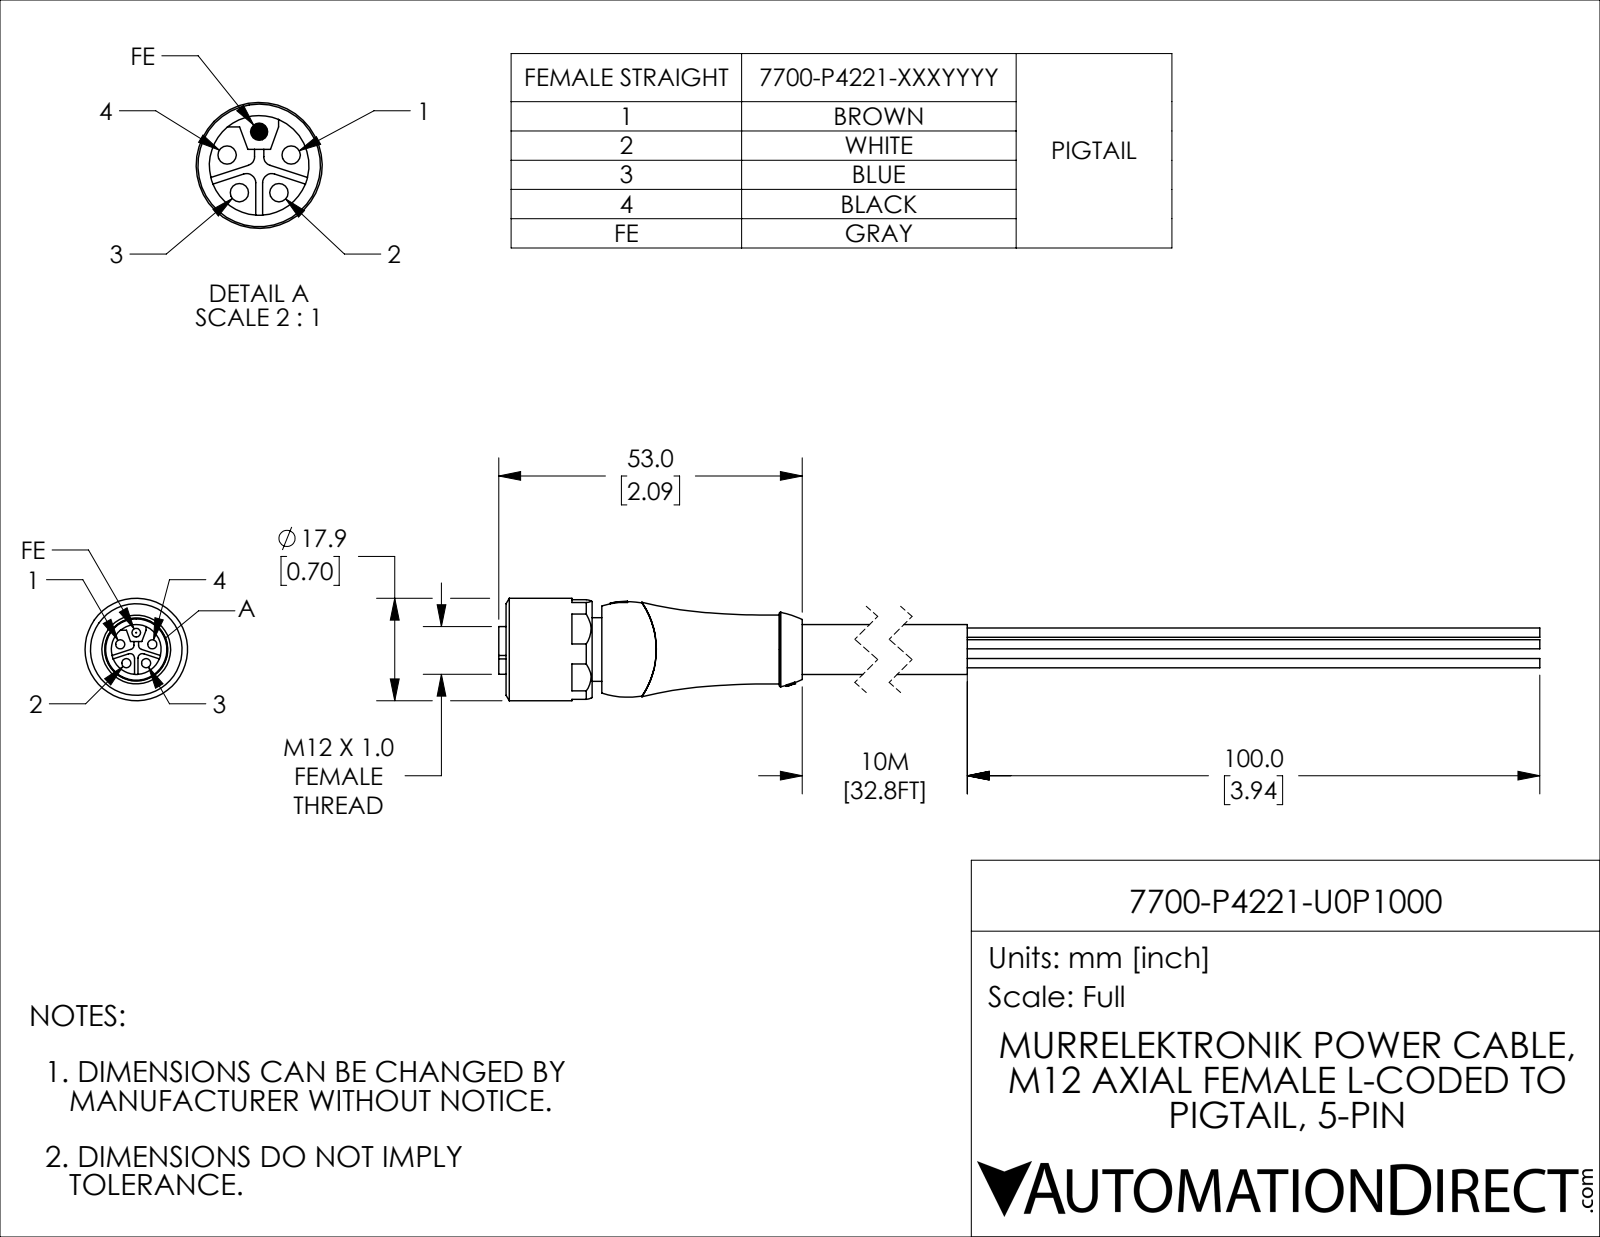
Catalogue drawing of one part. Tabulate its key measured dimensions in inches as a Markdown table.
| quantity | value |
| --- | --- |
| part name | 7700-P4221-U0P1000 |
| STEP written by | SolidWorks 2021 (CONFIG_CONTROL_DESIGN) |
| units | inches |
| bodies | 2 solids, 142 faces (69 planar, 40 cylindrical, 33 other) |
| overall size | 7.598 × 0.705 × 0.705 |
| volume | 0.735 in³ |
| surface area | 12.83 in² |
| round holes (diameter × count) | 0.063 × 4, 0.433 × 1, 0.512 × 1 |
| round bosses / shafts (diameter × count) | 0.705 × 1, 0.51 × 1, 0.437 × 1, 0.343 × 1, 0.063 × 1, 0.059 × 1 |
| partial cylindrical surfaces (radius × count) | 0.031 × 4 |
| main face-to-face distances | 0.657, 0.591, 0.067, 0.667, 3.61, 3.02, 2.953, 0.181, 0.362, 0.228 |
| hole center spacings | 0.116, 0.136, 0.22 |
